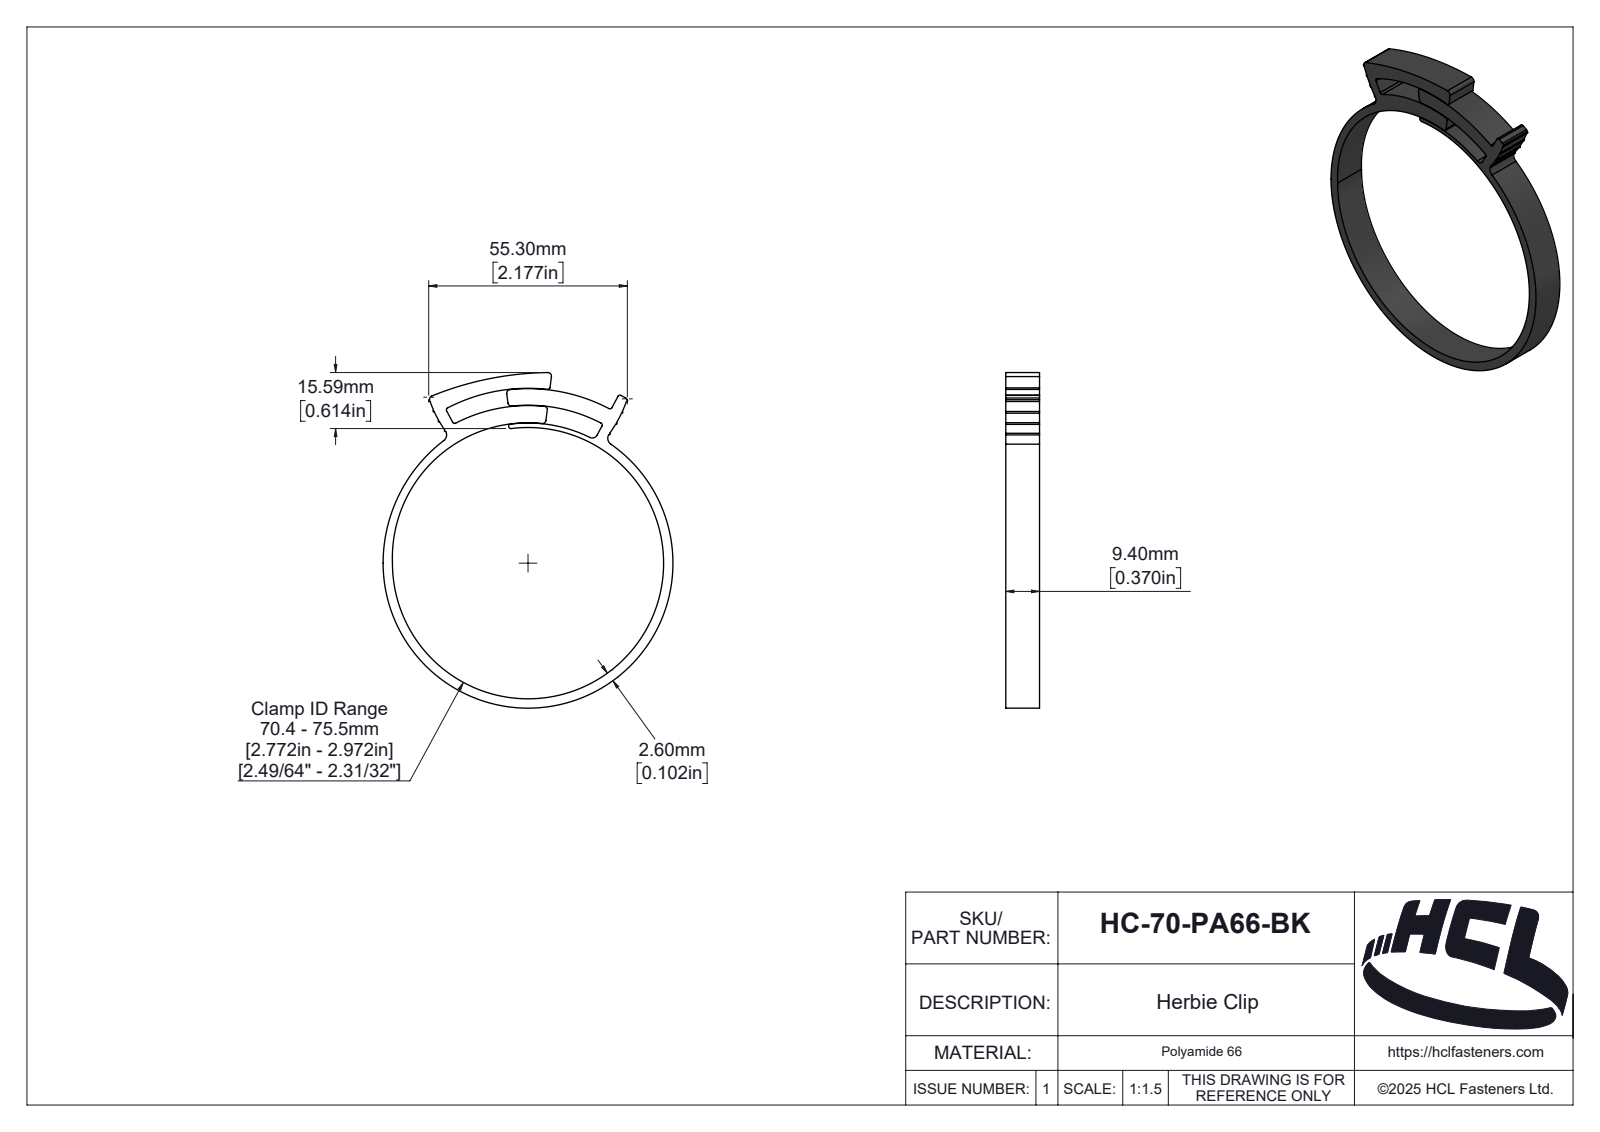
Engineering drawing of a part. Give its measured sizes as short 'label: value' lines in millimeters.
name: HC-70-PA66-BK
written by: SolidWorks 2025 (AUTOMOTIVE_DESIGN)
unit: mm
bodies: 1 solid, 162 faces (13 planar, 100 cylindrical, 49 other)
size: 93.39 × 80.7 × 9.4
volume: 9 589 mm³; area: 8 487 mm²
rounds: 8× R0.25, 6× R0.6, 5× R1, 2× R2, 1× R0.17, 1× R0.62, 1× R0.67, 1× R0.84
face distances: 9.4
